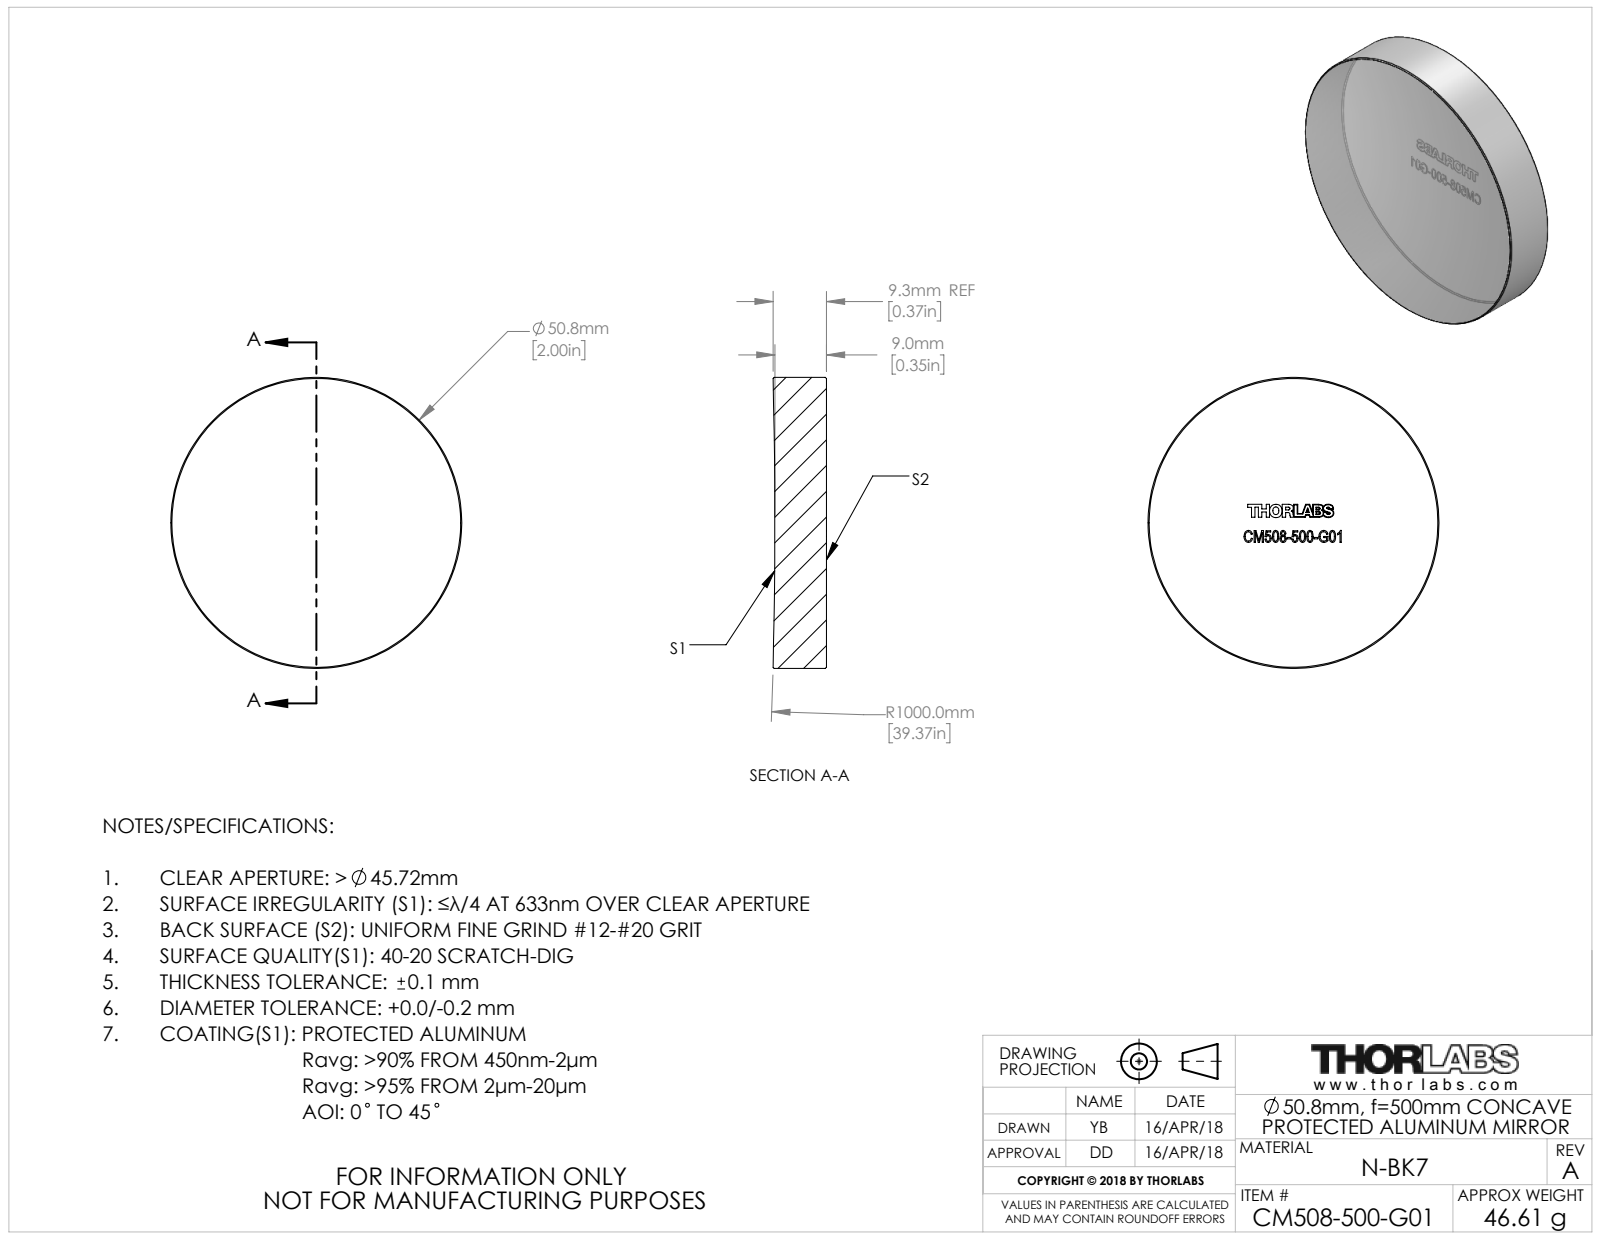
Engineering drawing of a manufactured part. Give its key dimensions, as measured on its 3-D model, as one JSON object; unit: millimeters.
{"part_name": "TTN153322-E0W", "step_written_by": "SolidWorks 2018 (CONFIG_CONTROL_DESIGN)", "units": "millimeters", "bodies": {"solids": 1, "faces": 43, "planar": 35, "cylindrical": 2, "other": 6}, "overall_size": [50.8, 50.8, 9.32], "volume_mm3": 18562, "surface_area_mm2": 5504, "round_bosses_or_shafts": [[50.8, 1]]}
